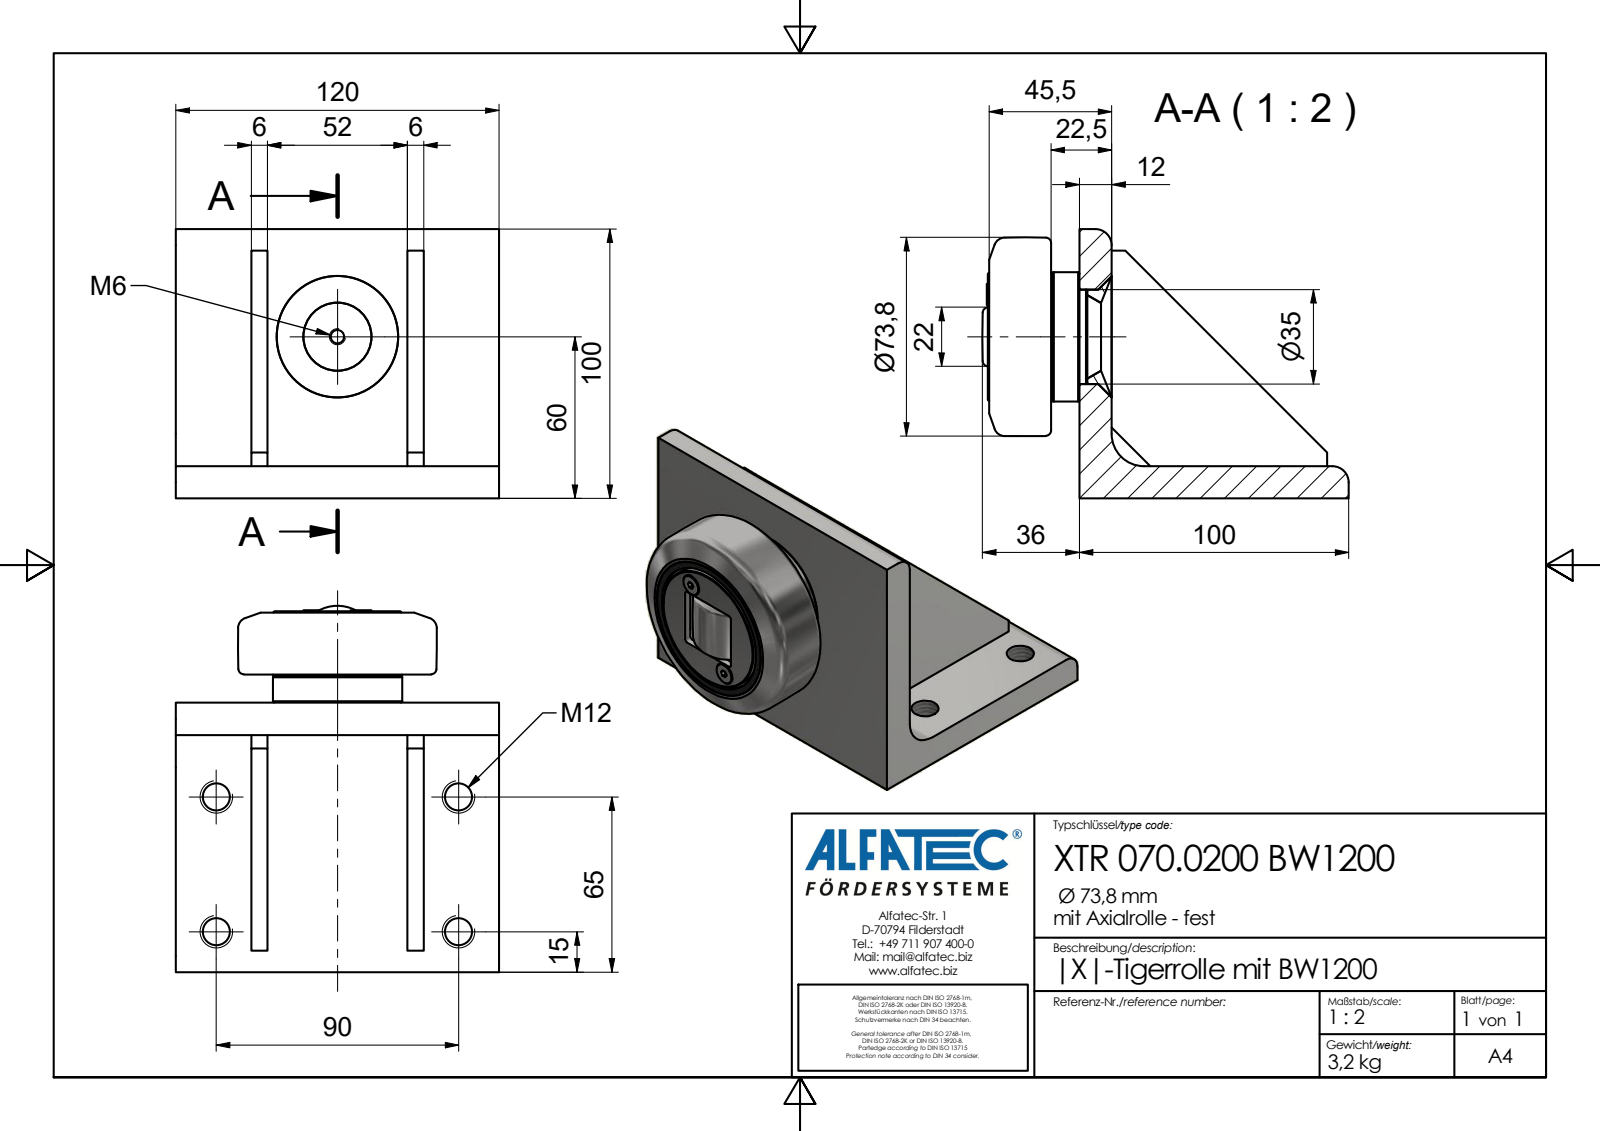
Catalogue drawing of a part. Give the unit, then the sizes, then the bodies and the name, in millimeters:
Units: millimetres
Overall size (bounding box): 136 × 120 × 100
Round holes (diameter × count): ⌀10.11 ×4, ⌀2.5 ×1, ⌀4.92 ×1
Round bosses / shafts (diameter × count): ⌀7.8 ×2, ⌀48 ×1, ⌀47.3 ×1
Partial cylindrical surfaces — rounded edges, fillets, slot ends (radius × count): R1 ×4, R6 ×2, R12 ×1
Main face-to-face distances: 12, 6, 58, 34, 92, 28, 86, 64, 52, 120
Hole centre spacings: 50, 90, 102.96
Volume: 421 430 mm³ · Surface area: 77 824 mm²
Bodies: 1 solid, 81 faces (50 planar, 18 cylindrical, 13 other)
Part name (STEP PRODUCT): XTR 070.0200 BW1200_Kontur
STEP written by: Autodesk Inventor 2020 (AP242_MANAGED_MODEL_BASED_3D_ENGINEERING_MIM_LF)
